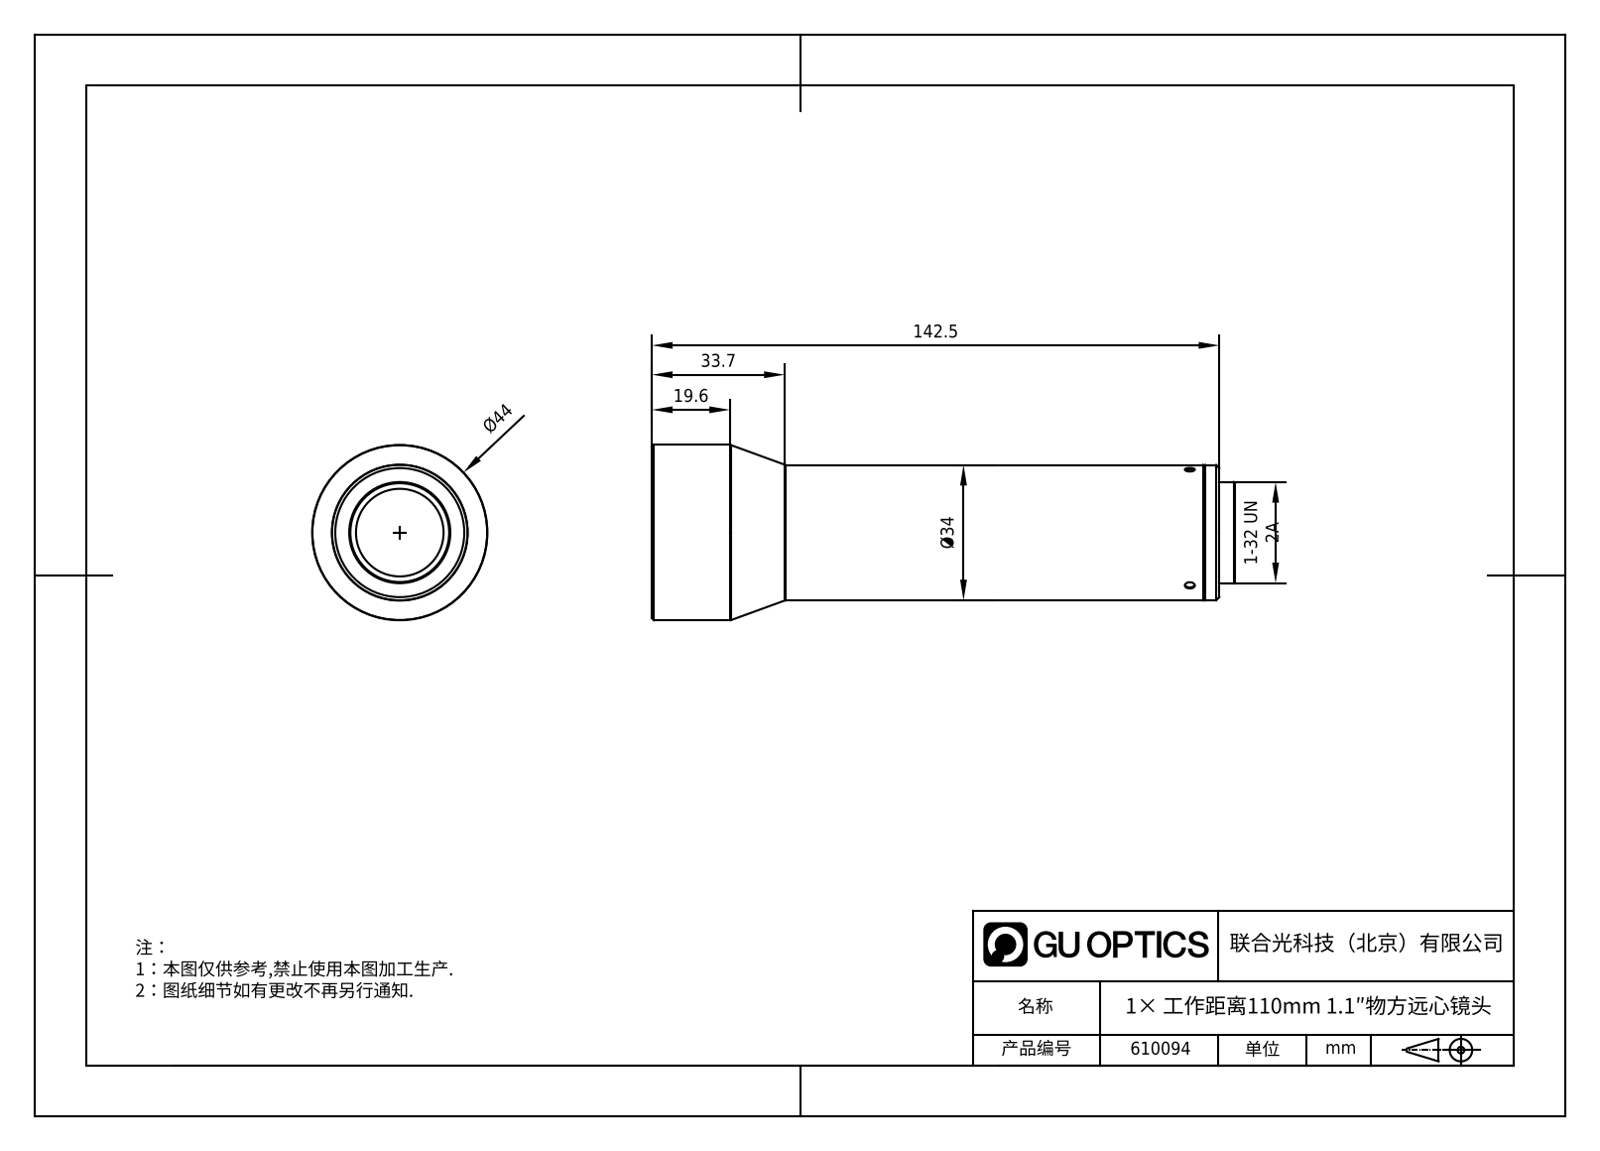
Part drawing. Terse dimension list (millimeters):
name: WWK10-110-111V3
written by: SolidWorks 2017 (CONFIG_CONTROL_DESIGN)
unit: mm
bodies: 1 solid, 56 faces (15 planar, 23 cylindrical, 18 other)
size: 146.39 × 44 × 44
volume: 140 686 mm³; area: 19 656 mm²
holes: 3× ⌀2.5, 1× ⌀22, 1× ⌀40.5
bosses: 1× ⌀44, 1× ⌀34, 1× ⌀33.28, 1× ⌀25.4
face distances: 137.28, 138.69, 1.41, 3.8, 141.08, 142.49, 2.7, 1.1, 138.38, 139.79
